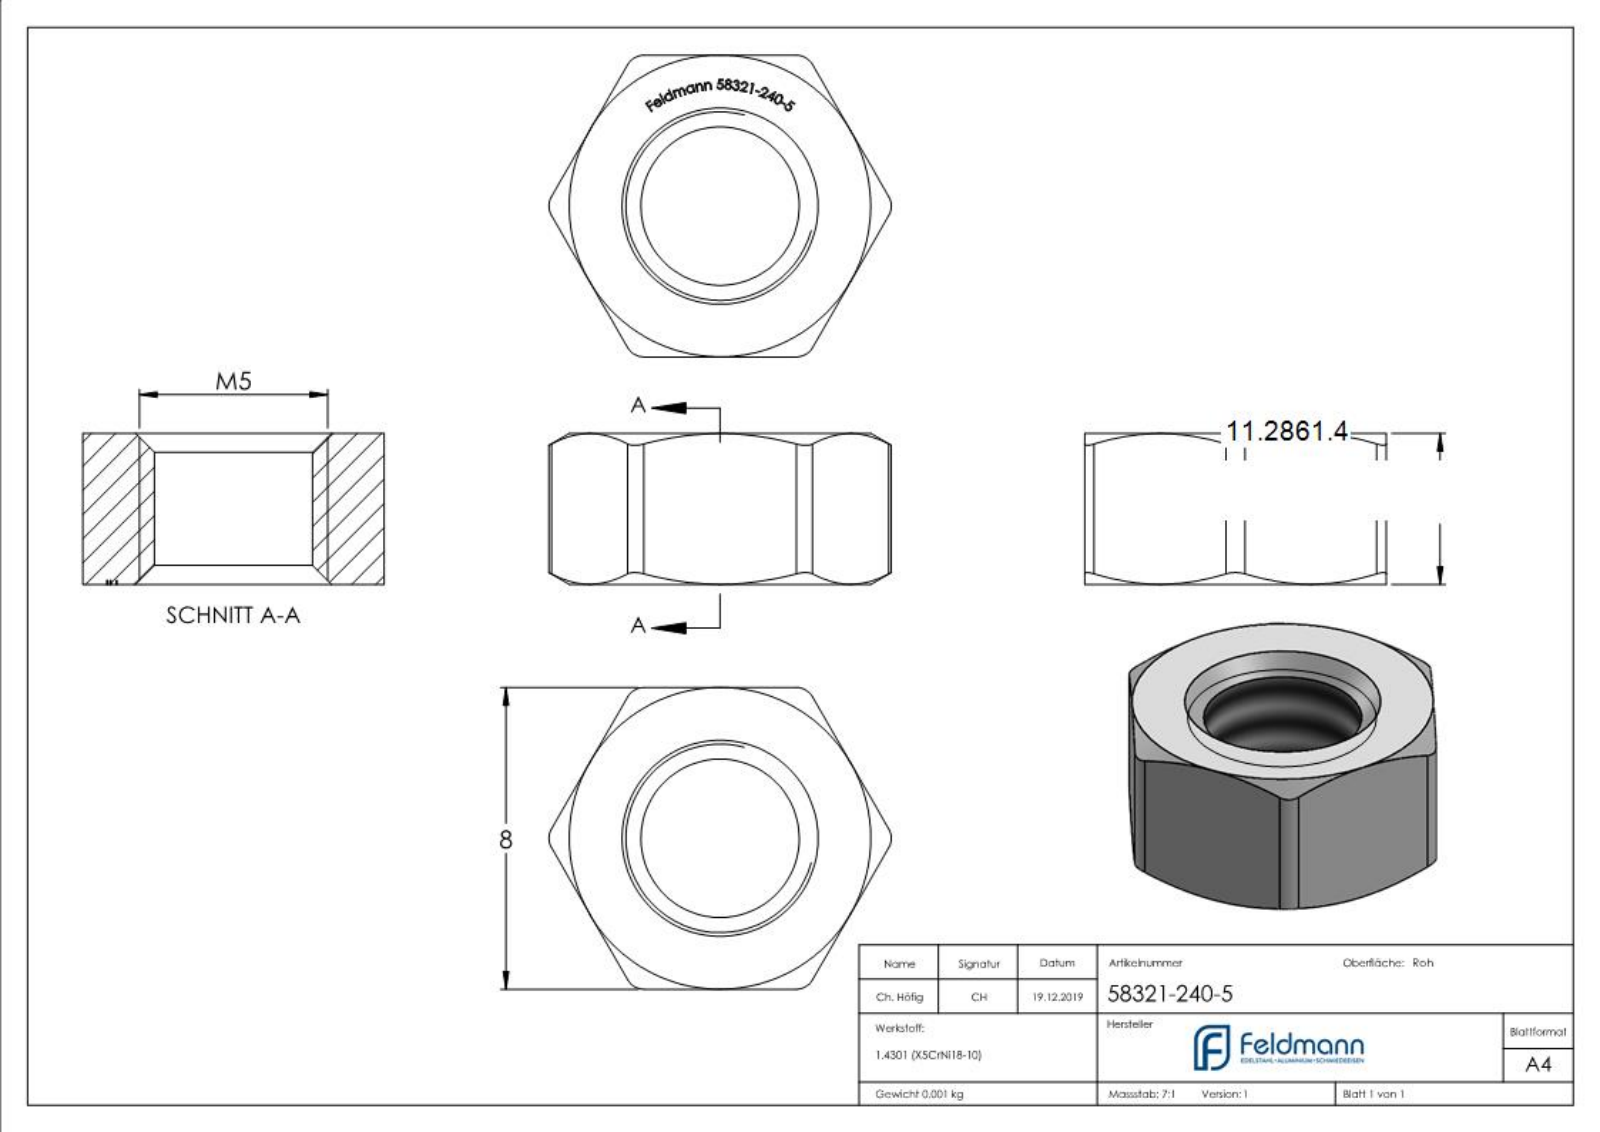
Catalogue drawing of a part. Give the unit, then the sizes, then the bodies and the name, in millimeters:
Units: millimetres
Overall size (bounding box): 22 × 9.08 × 8
Round holes (diameter × count): ⌀4.2 ×1
Partial cylindrical surfaces — rounded edges, fillets, slot ends (radius × count): R0.5 ×6
Main face-to-face distances: 8, 4
Volume: 161 mm³ · Surface area: 233 mm²
Bodies: 1 solid, 29 faces (8 planar, 7 cylindrical, 14 other)
Part name (STEP PRODUCT): 58321-240-5
STEP written by: SolidWorks 2015 (CONFIG_CONTROL_DESIGN)
